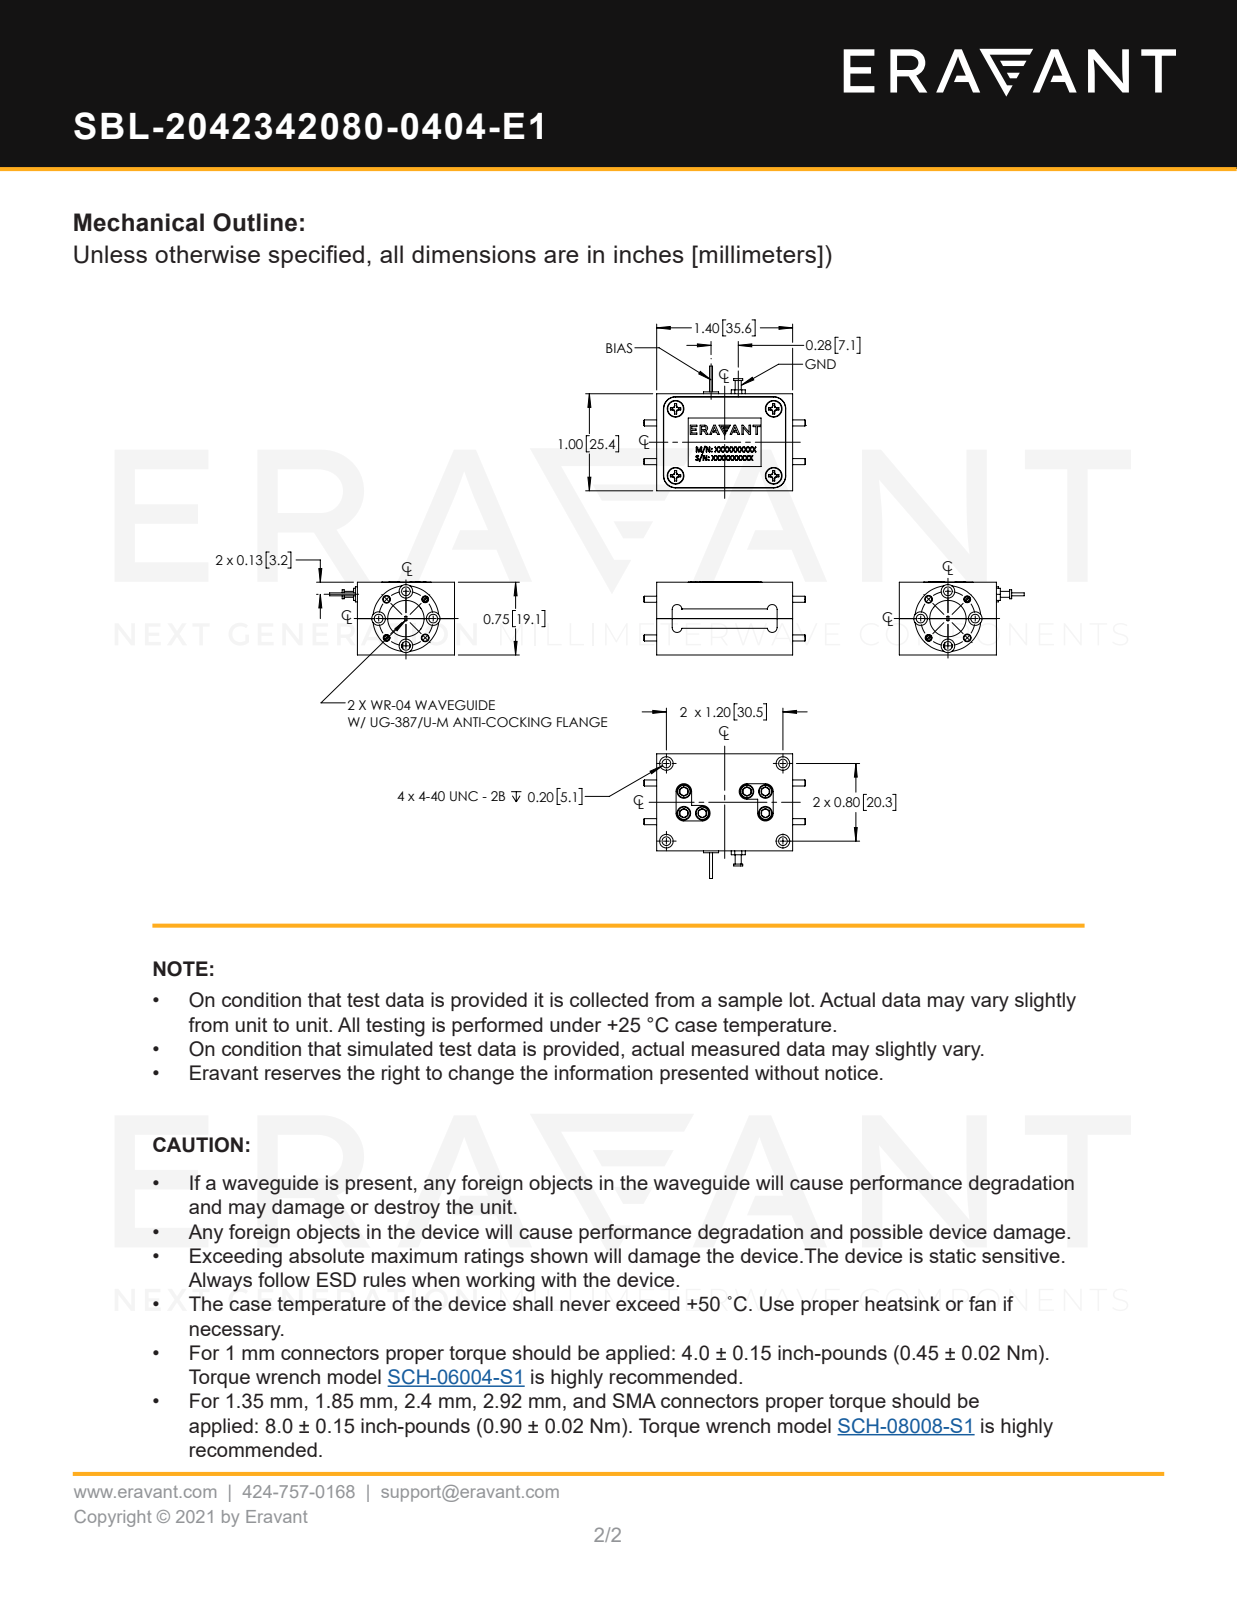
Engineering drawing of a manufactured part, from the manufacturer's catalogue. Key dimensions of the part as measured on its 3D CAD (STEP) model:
Part name (STEP PRODUCT): BG-S04-2-A, Defeatured
STEP written by: SolidWorks 2021 (AUTOMOTIVE_DESIGN)
Units: inches
Bodies: 7 solids, 415 faces (185 planar, 138 cylindrical, 92 other)
Overall size (bounding box): 1.665 × 1.285 × 0.75
Volume: 0.876 in³ · Surface area: 13.75 in²
Round holes (diameter × count): ⌀0.089 ×8, ⌀0.14 ×8, ⌀0.061 ×4, ⌀0.067 ×4, ⌀0.07 ×4, ⌀0.043 ×1, ⌀0.68 ×1
Round bosses / shafts (diameter × count): ⌀0.063 ×4, ⌀0.375 ×1, ⌀0.156 ×1, ⌀0.093 ×1, ⌀0.062 ×1, ⌀0.03 ×1
Partial cylindrical surfaces — rounded edges, fillets, slot ends (radius × count): R0.05 ×4, R0.054 ×4, R0.122 ×4, R0.125 ×4
Main face-to-face distances: 0.04, 0.71, 0.75, 0.375, 0.335, 0.375, 0.1, 1, 0.2, 0.275
Hole centre spacings: 0.215, 0.52, 0.398, 0.281, 0.281, 0.563, 0.398, 0.11
